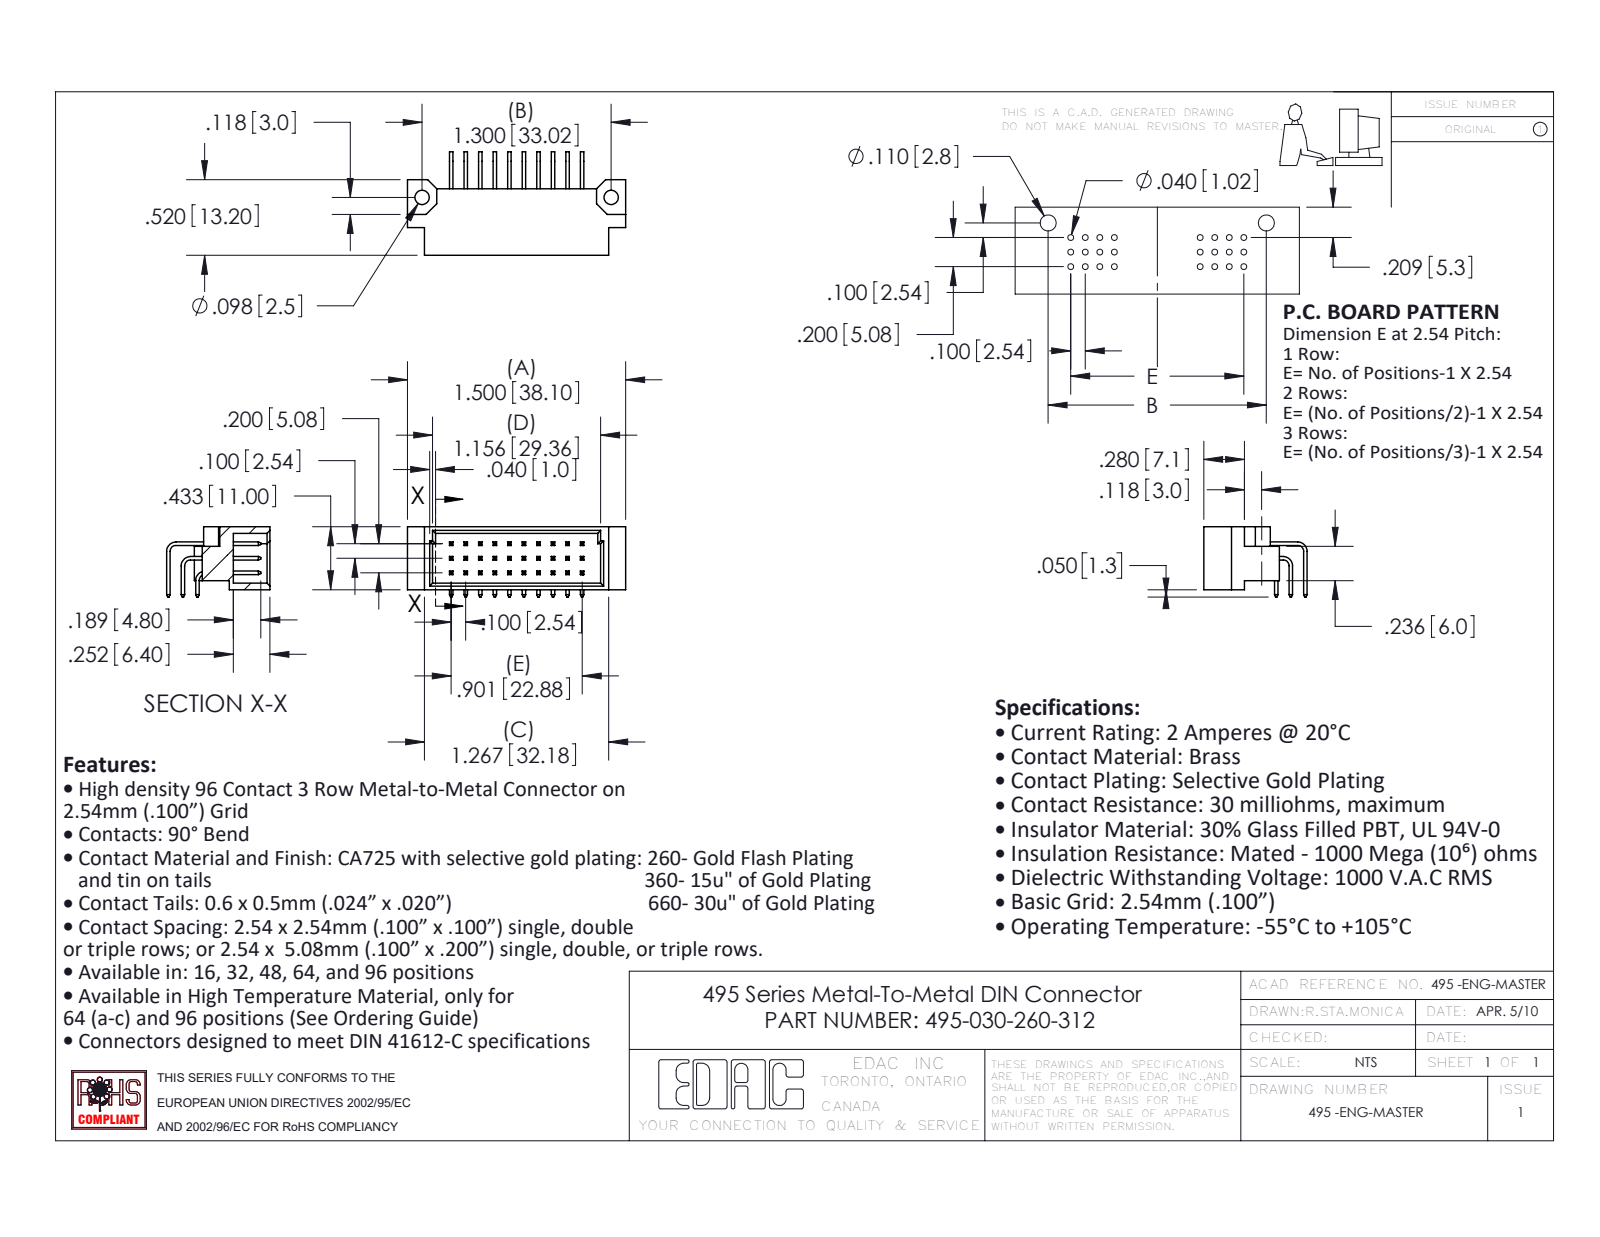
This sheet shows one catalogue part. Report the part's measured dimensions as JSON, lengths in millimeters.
{"part_name": "495-290-1; 495-290-2; 495 Part_30; 495-290-3 (+1 more)", "step_written_by": "SolidWorks 2020 (AUTOMOTIVE_DESIGN)", "units": "millimeters", "bodies": {"solids": 31, "faces": 709, "planar": 645, "cylindrical": 64, "other": 0}, "overall_size": [38.1, 18.05, 12.27], "volume_mm3": 2676, "surface_area_mm2": 4287, "round_holes": [[2.49, 2]], "partial_cylinders_radius": [[1.02, 3], [1.65, 3]], "face_to_face_distances": [2.54, 5.08, 7.62, 9.86, 0.61, 10.16, 5.2, 1.14, 12.7, 0.6], "hole_center_spacings": [33.02]}
